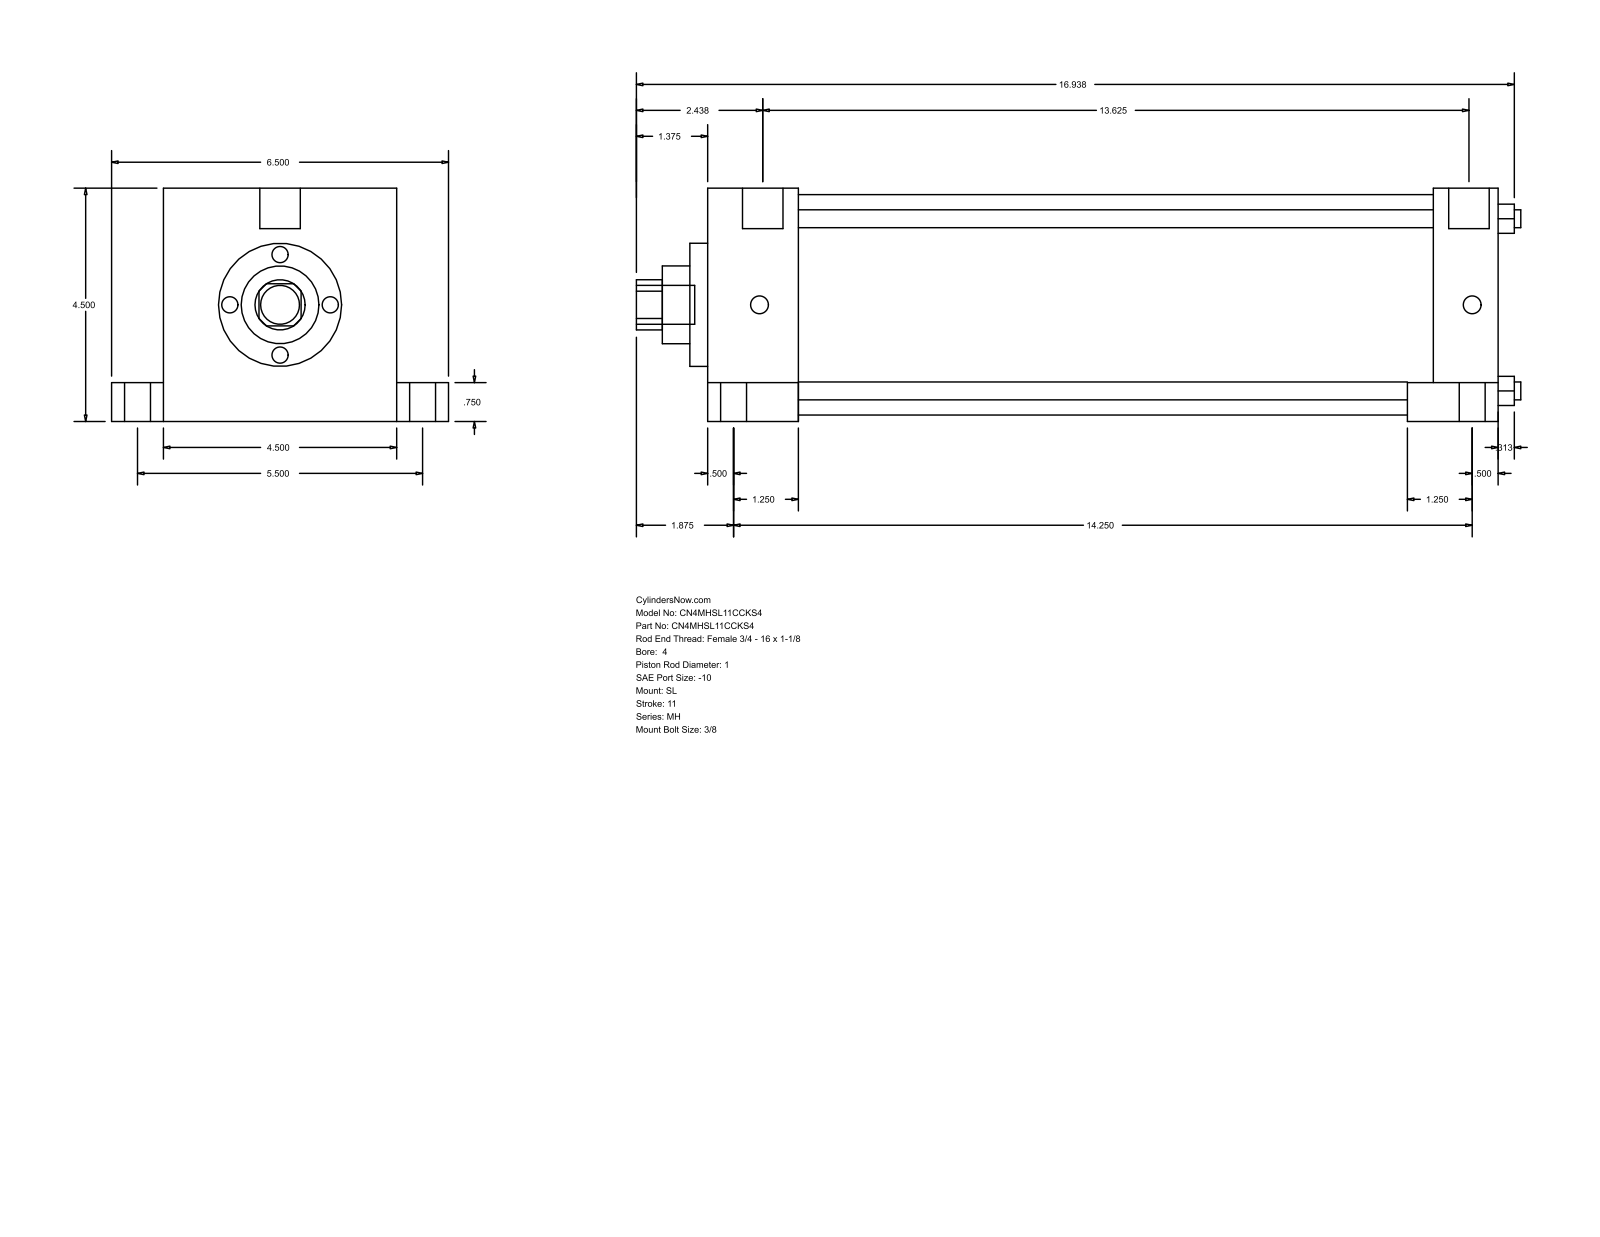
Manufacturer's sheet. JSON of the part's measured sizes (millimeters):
{"part_name": "MH_SL__0400_1", "step_written_by": "GSSL Pune (CONFIG_CONTROL_DESIGN)", "units": "millimeters", "bodies": {"solids": 0, "faces": 110, "planar": 77, "cylindrical": 33, "other": 0}, "overall_size": [433.39, 165.1, 114.3], "round_holes": [[8.76, 4], [25.4, 1], [38.1, 1], [60.33, 1], [107.95, 1]], "round_bosses_or_shafts": [[19.05, 5], [12.7, 4], [8.73, 4], [19.84, 2]], "partial_cylinders_radius": [[12.29, 1]], "face_to_face_distances": [114.3, 387.35, 44.46, 342.89, 355.6, 311.14, 31.75, 25.4, 139.7, 19.05], "hole_center_spacings": [59.62, 84.32, 119.25]}
